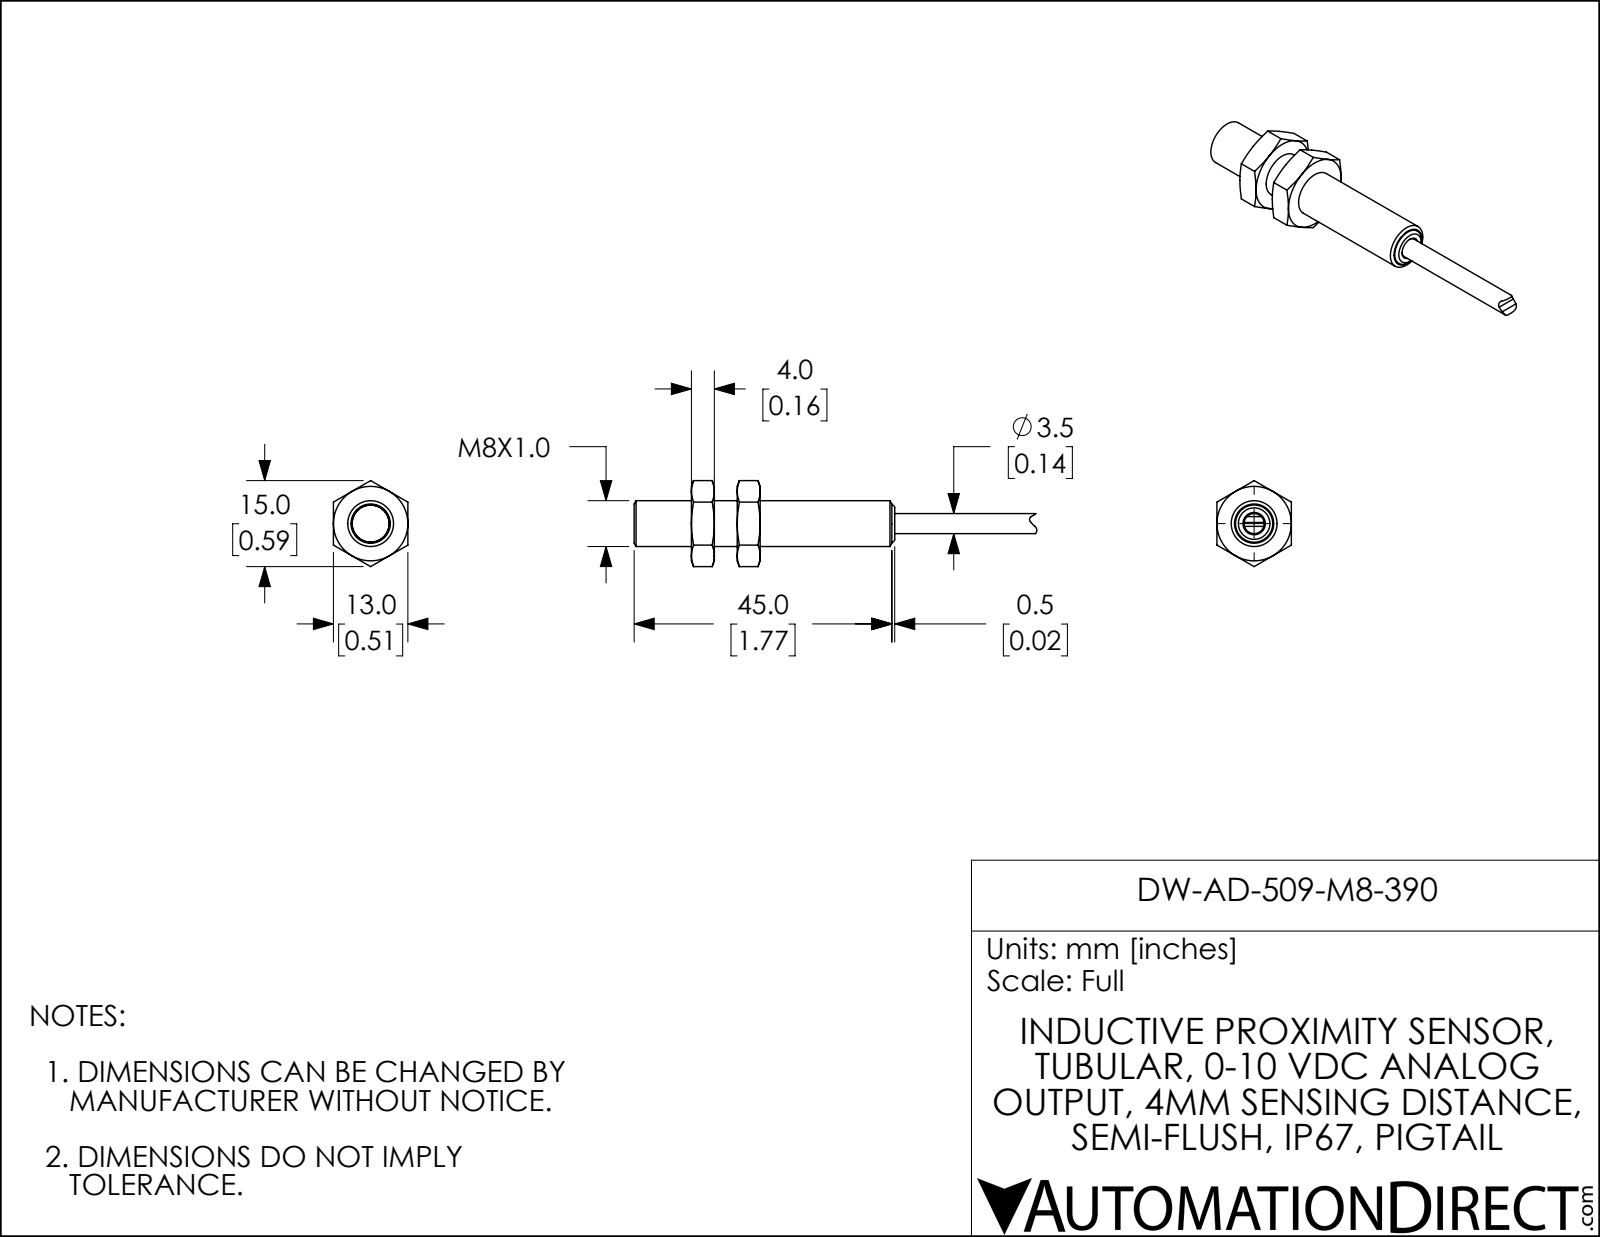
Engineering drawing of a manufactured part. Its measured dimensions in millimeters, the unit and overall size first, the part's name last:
Units: millimetres
Overall size (bounding box): 70.3 × 15 × 13
Round bosses / shafts (diameter × count): ⌀8 ×1, ⌀6.5 ×1, ⌀3.5 ×1
Partial cylindrical surfaces — rounded edges, fillets, slot ends (radius × count): R0.6 ×1, R0.8 ×1, R3.4 ×1, R5.1 ×1
Main face-to-face distances: 4, 13, 8, 12, 10, 14, 18, 22, 45.5, 35.5
Volume: 3 260 mm³ · Surface area: 2 026 mm²
Bodies: 1 solid, 59 faces (21 planar, 9 cylindrical, 29 other)
Part name (STEP PRODUCT): DW-AD-509-M8-390
STEP written by: SolidWorks 2018 (AUTOMOTIVE_DESIGN)
